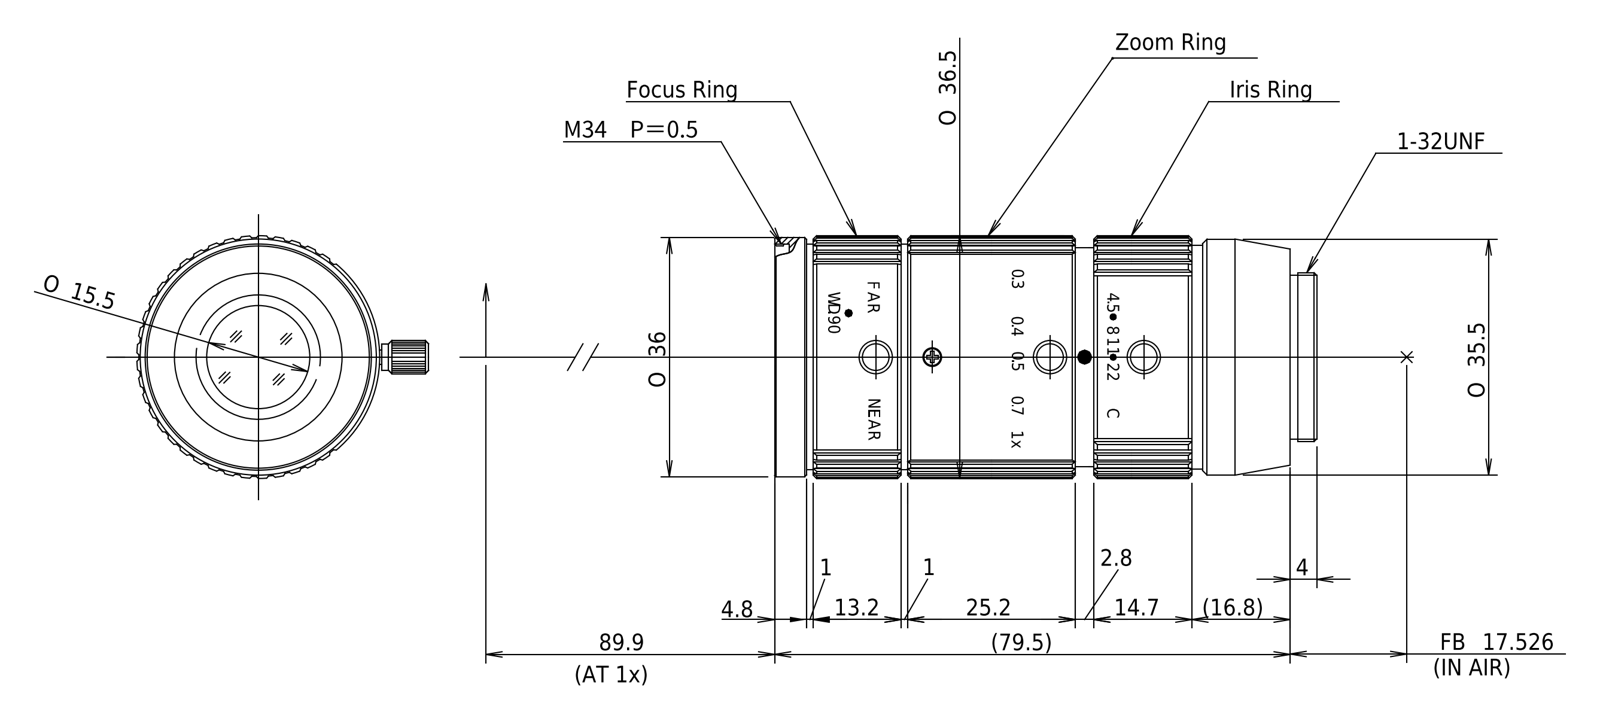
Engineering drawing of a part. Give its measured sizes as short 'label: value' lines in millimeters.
name: MLM-3XMP_210601
written by: ST-DEVELOPER v16.7 (AUTOMOTIVE_DESIGN)
unit: mm
bodies: 1 solid, 473 faces (259 planar, 190 cylindrical, 24 other)
size: 81.5 × 43.85 × 36.5
volume: 100 144 mm³; area: 17 818 mm²
holes: 1× ⌀18.7, 1× ⌀21.7, 1× ⌀23, 1× ⌀25, 1× ⌀33.4, 1× ⌀34
bosses: 3× ⌀5, 3× ⌀4, 3× ⌀2.2, 1× ⌀36.5, 1× ⌀36, 1× ⌀35.5, 1× ⌀33.9, 1× ⌀33.6
rounds: 35× R230.47
face distances: 1, 74.27, 75.27, 57.5, 2.8, 14.2, 71.7, 42.97, 31.3, 32.3
